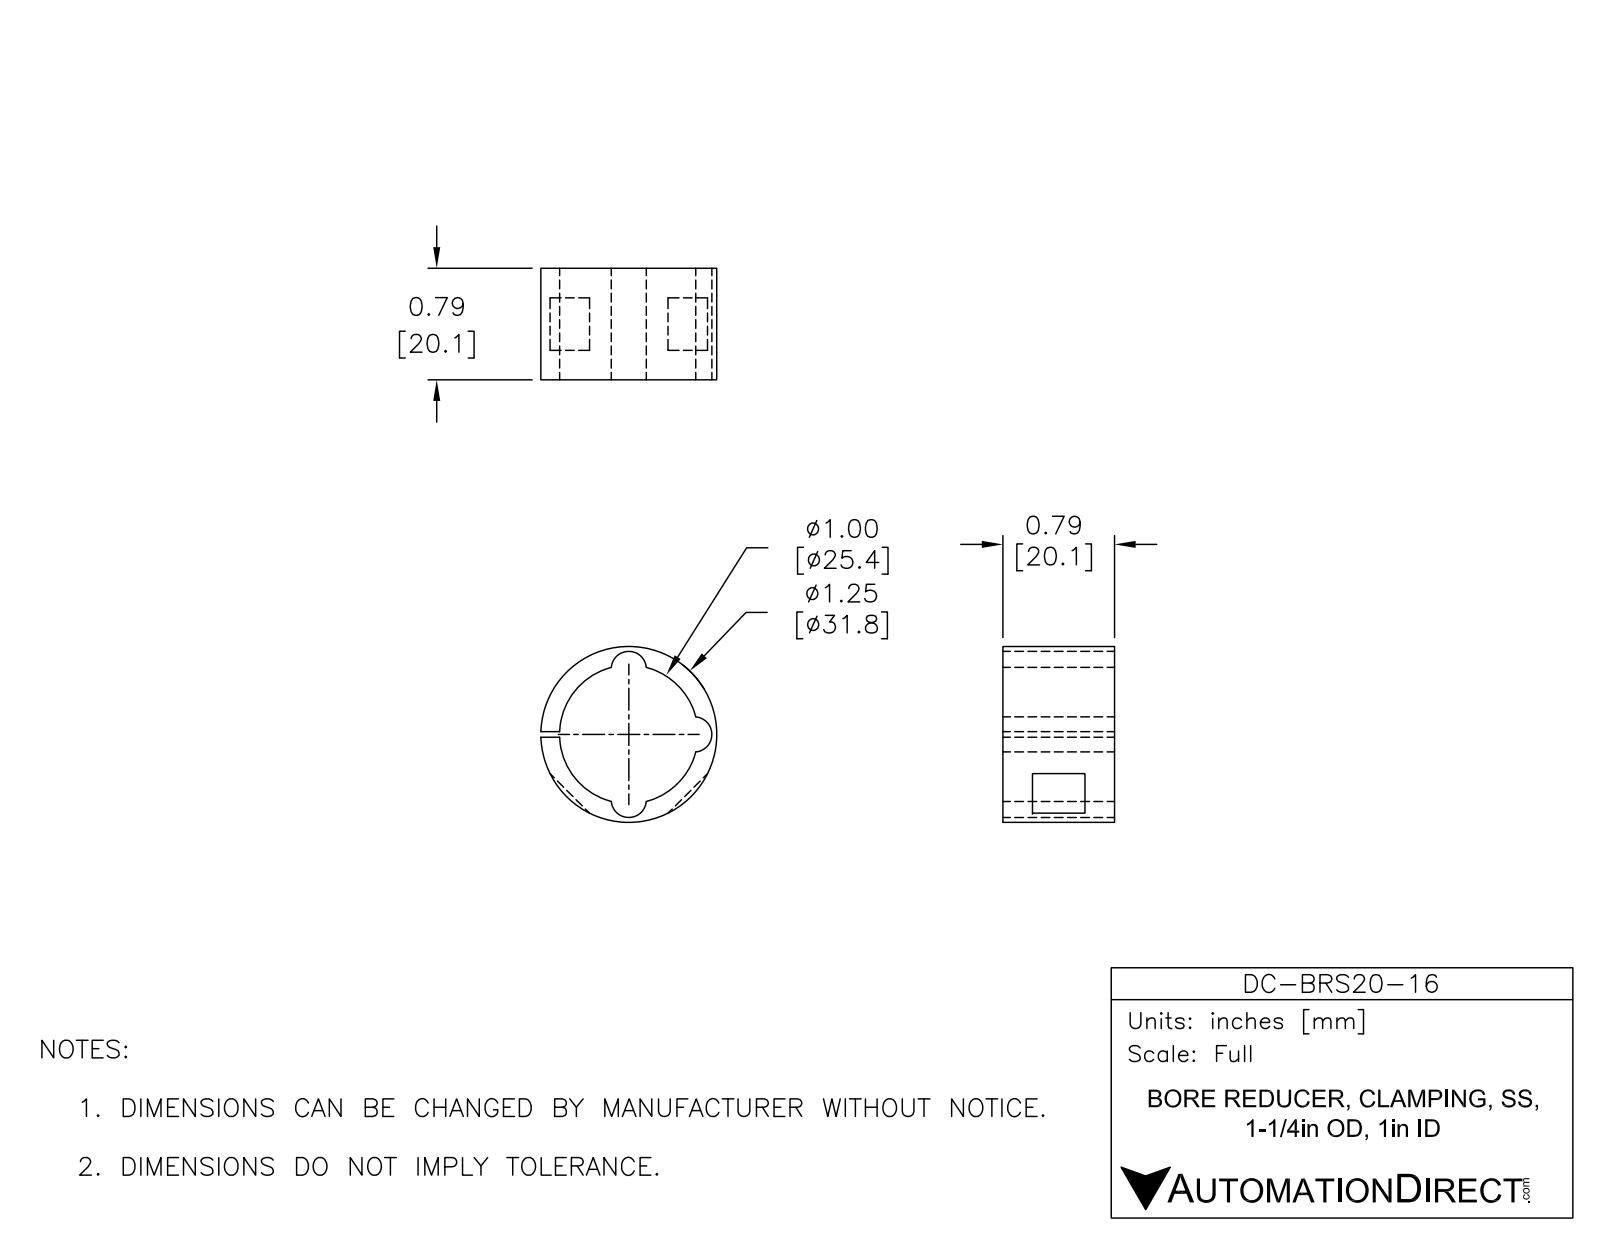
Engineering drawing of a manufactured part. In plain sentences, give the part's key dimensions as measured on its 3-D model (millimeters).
The part is named "DC-BRS20-16". Its 3-D file was written by "SolidWorks 2015 (AUTOMOTIVE_DESIGN)". It is 1 solid with 21 faces: 10 planar, 11 cylindrical and 0 other. Overall it measures 31.75 by 31.74 by 20.14 millimeters. Its volume is 2 765 cubic millimeters and its surface area 4 170 square millimeters. Round holes: 1 of diameter 28.58. Round bosses or shafts: 1 of diameter 31.75. Partial cylindrical surfaces (rounded edges, fillets, slot ends): 3 of radius 3.17. The main face-to-face distances are 20.14, 1.02, 5.33, 14.81, 9.48.
